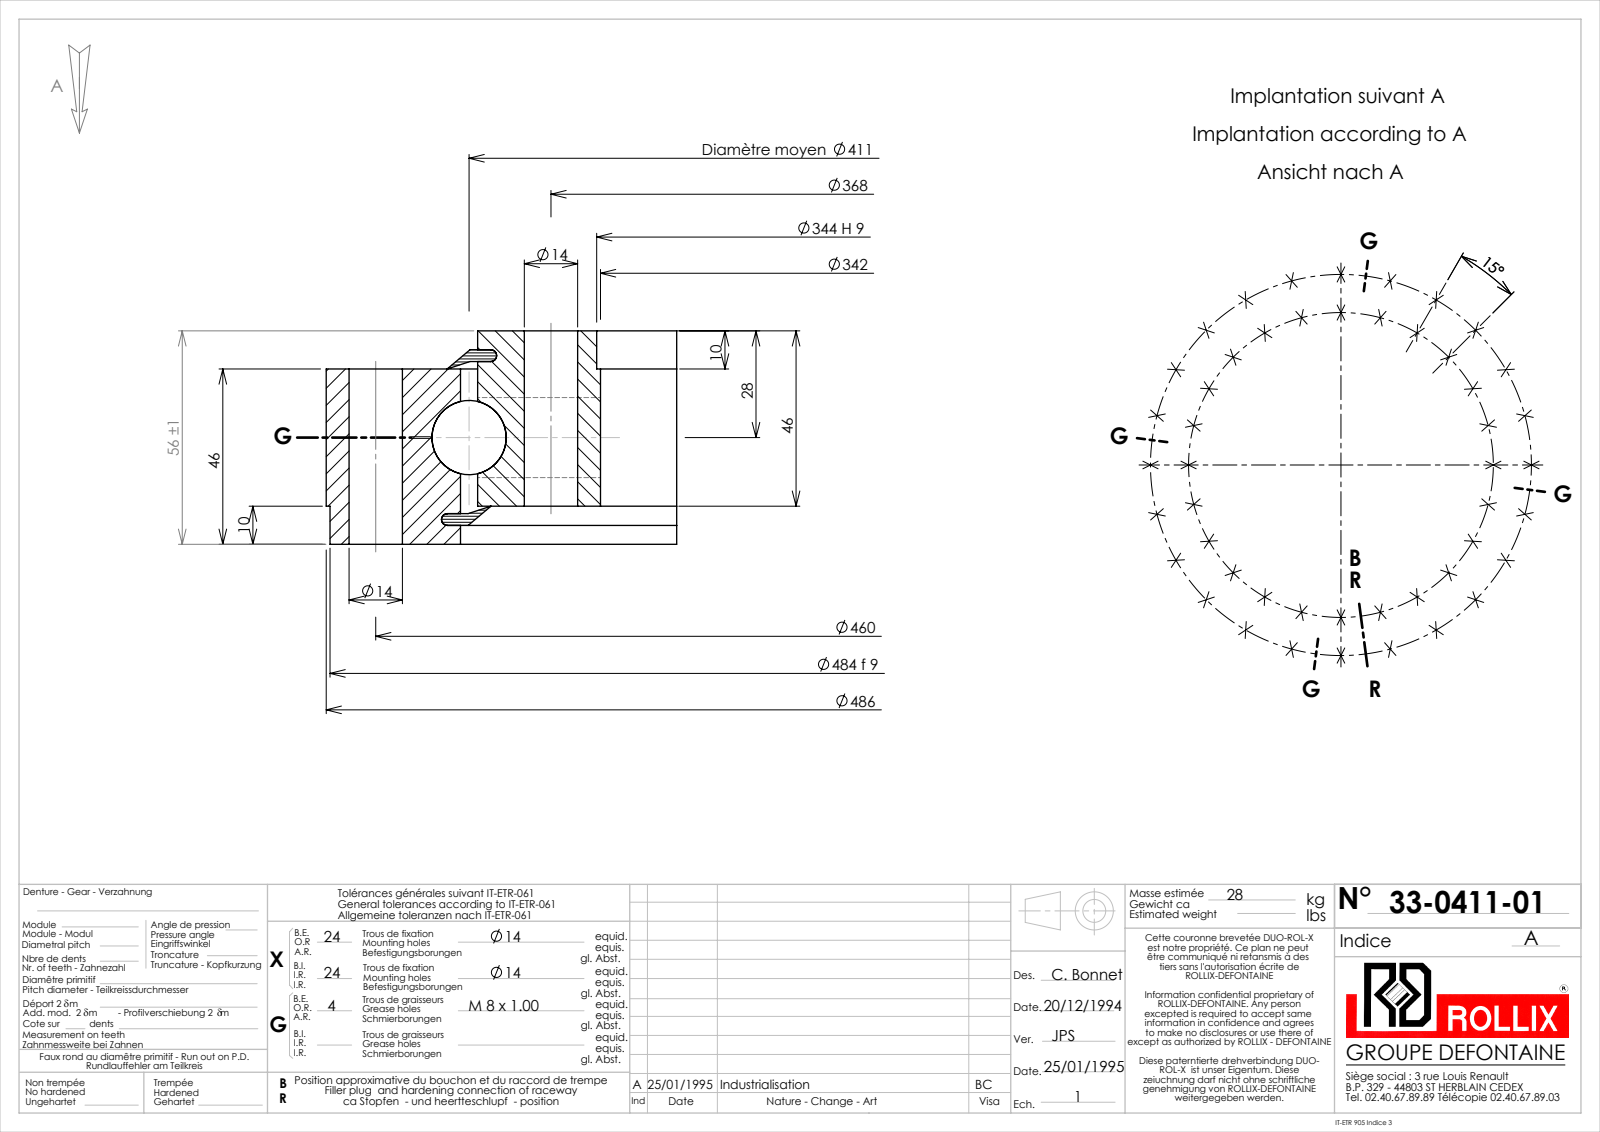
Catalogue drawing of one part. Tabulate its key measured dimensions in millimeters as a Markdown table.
| quantity | value |
| --- | --- |
| part name | 33-0411-01 |
| STEP written by | SolidWorks 2016 (CONFIG_CONTROL_DESIGN) |
| units | millimeters |
| bodies | 9 solids, 254 faces (54 planar, 132 cylindrical, 68 other) |
| overall size | 501.3 × 501.3 × 56 |
| volume | 3 443 000 mm³ |
| surface area | 619 694 mm² |
| round holes (diameter × count) | 14 × 48, 7 × 4, 342 × 1, 344 × 1, 415.5 × 1 |
| round bosses / shafts (diameter × count) | 8 × 4, 486 × 1, 484 × 1, 406.5 × 1 |
| main face-to-face distances | 46, 10, 36, 56, 4.95, 51.05, 5.05, 41.05, 8.05, 47.95 |
| hole center spacings | 184, 339.99, 355.46, 95.25, 318.7, 48.03, 140.83, 224.03 |
